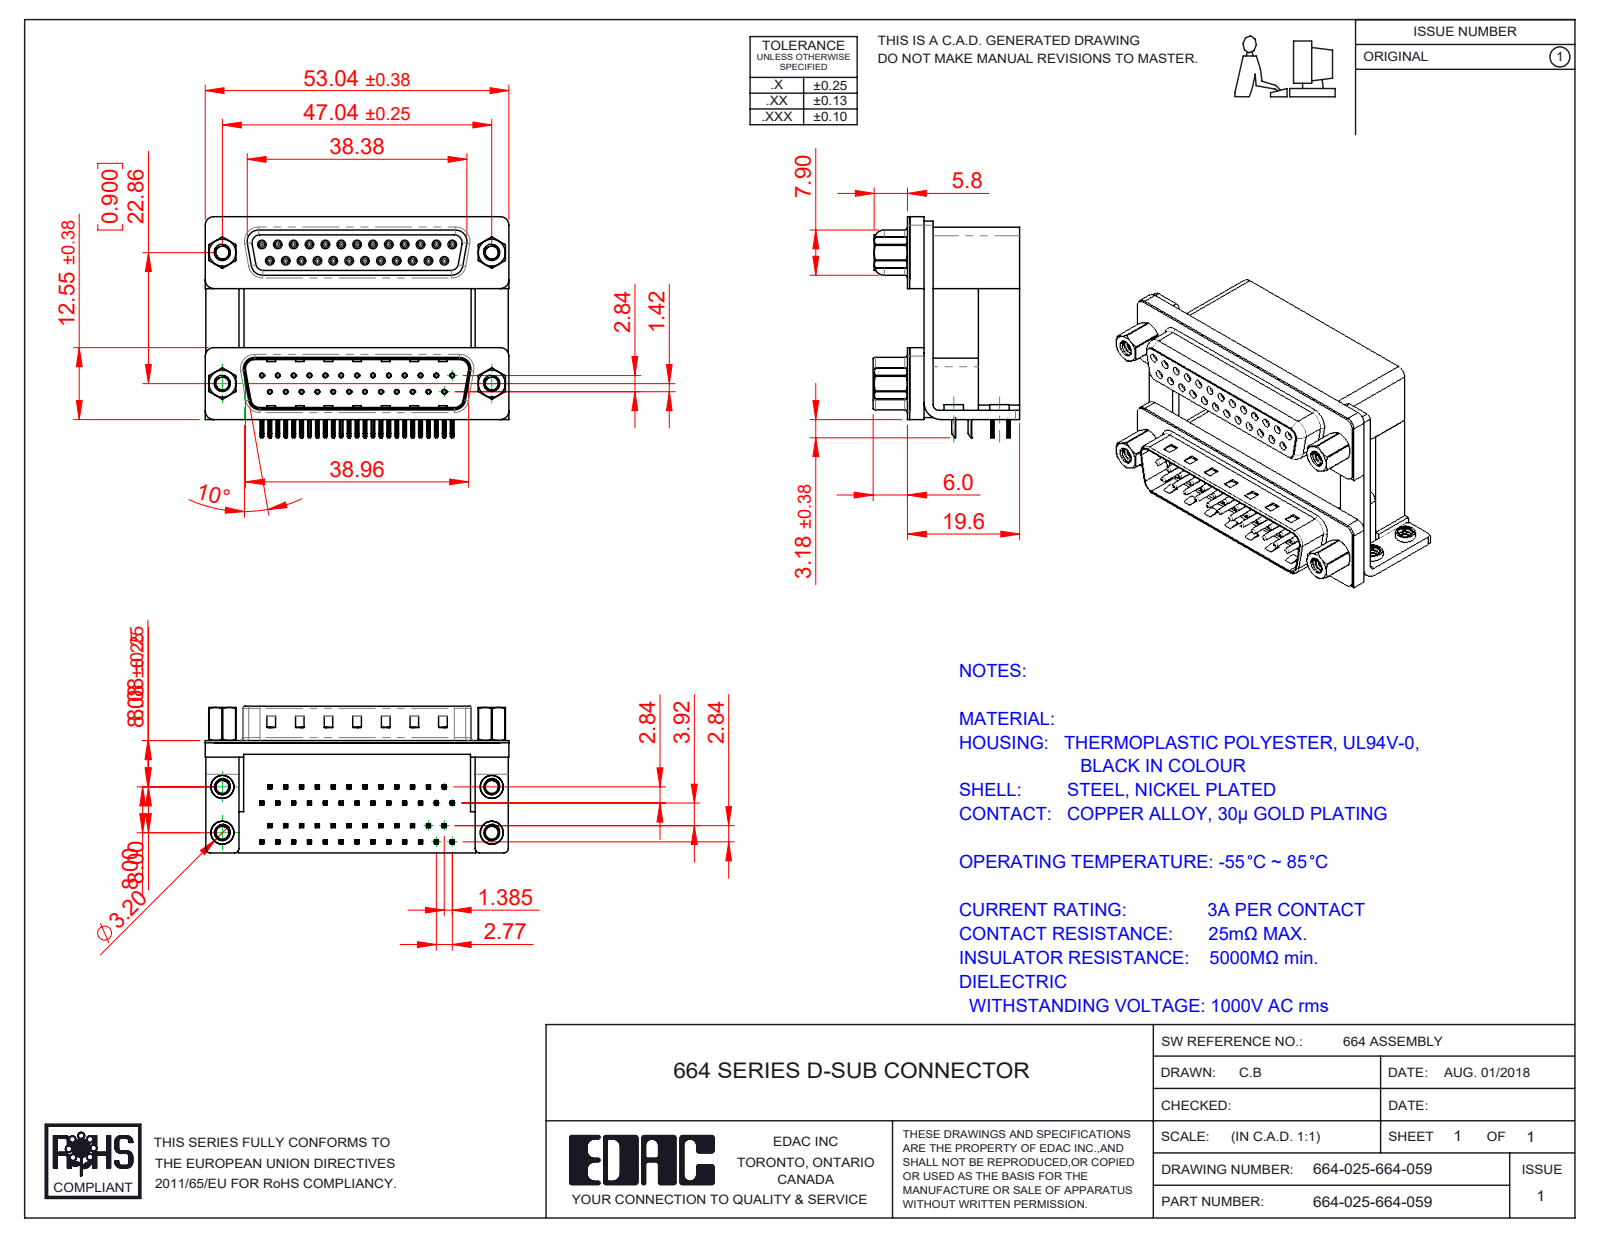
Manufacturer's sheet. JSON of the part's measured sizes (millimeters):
{"part_name": "664 Contact Top Upper_H; 664 Mounting Bracket_ThruH; 664 Contact Bottom Upper_H; 664 Threaded Rivet_4-40 (+8 more)", "step_written_by": "SolidWorks 2020 (CONFIG_CONTROL_DESIGN)", "units": "millimeters", "bodies": {"solids": 69, "faces": 6595, "planar": 3313, "cylindrical": 1763, "other": 1519}, "overall_size": [53.04, 38.59, 25.6], "volume_mm3": 24090, "surface_area_mm2": 26324, "round_holes": [[0.8, 50], [0.35, 25], [0.9, 25], [2.26, 8], [2.29, 4], [2.75, 4], [3.2, 4], [3.5, 4], [4, 4], [4.8, 4], [5, 4]], "round_bosses_or_shafts": [[1.2, 25], [0.75, 25], [4.9, 4], [4.75, 4], [4, 4], [3.9, 4], [3.4, 4], [2.79, 4]], "partial_cylinders_radius": [[0.1, 200], [0.15, 100], [0.25, 100], [0.12, 50], [0.35, 50], [0.34, 25], [1.5, 14], [0.28, 12]], "face_to_face_distances": [19.2, 0.4, 12, 7.2, 10.7, 2.84, 16.7, 9.5, 2.5, 12.4], "hole_center_spacings": [2.77, 3.16, 5.54, 8.31, 11.08, 13.85, 16.62, 5.03]}
